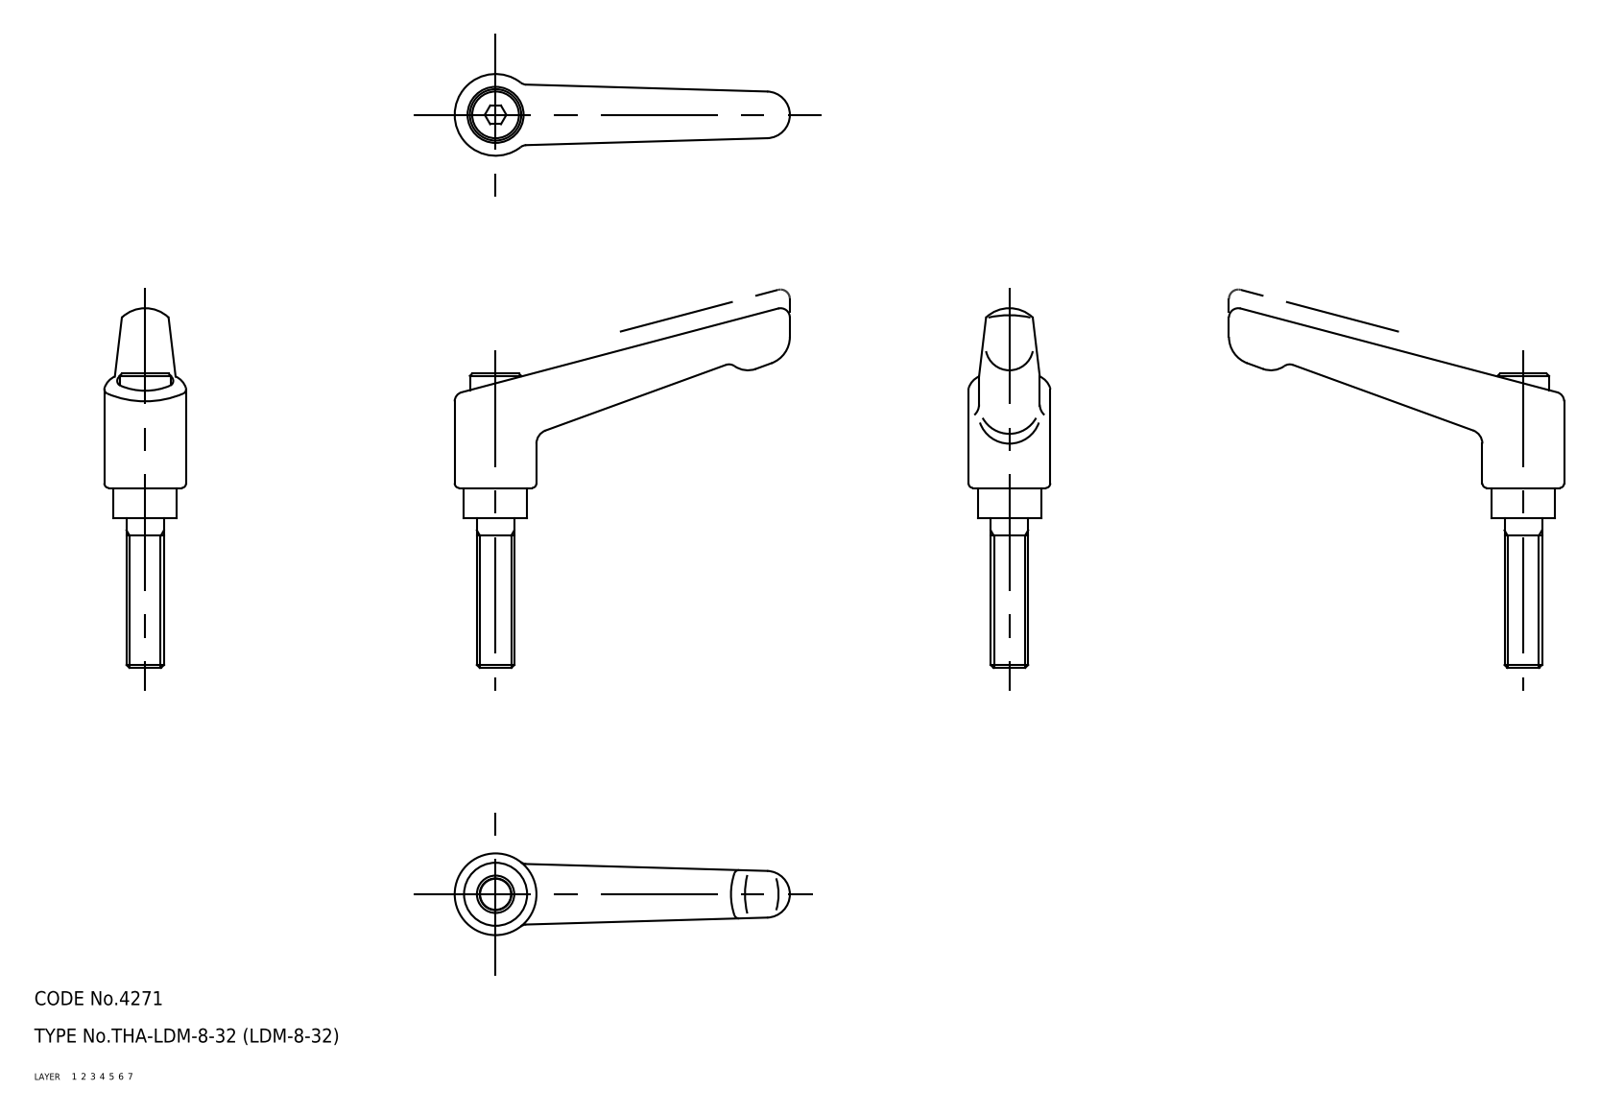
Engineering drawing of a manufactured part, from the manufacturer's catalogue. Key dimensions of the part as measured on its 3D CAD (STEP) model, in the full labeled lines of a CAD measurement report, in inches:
Part name (STEP PRODUCT): sleeve; screw; handle; LDM_8_32_26437_36
STEP written by: CADfix (AUTOMOTIVE_DESIGN)
Units: inches
Bodies: 3 solids, 75 faces (0 planar, 0 cylindrical, 75 other)
Overall size (bounding box): 3.031 × 2.825 × 0.689
Volume: 0.837 in³ · Surface area: 10.57 in²
